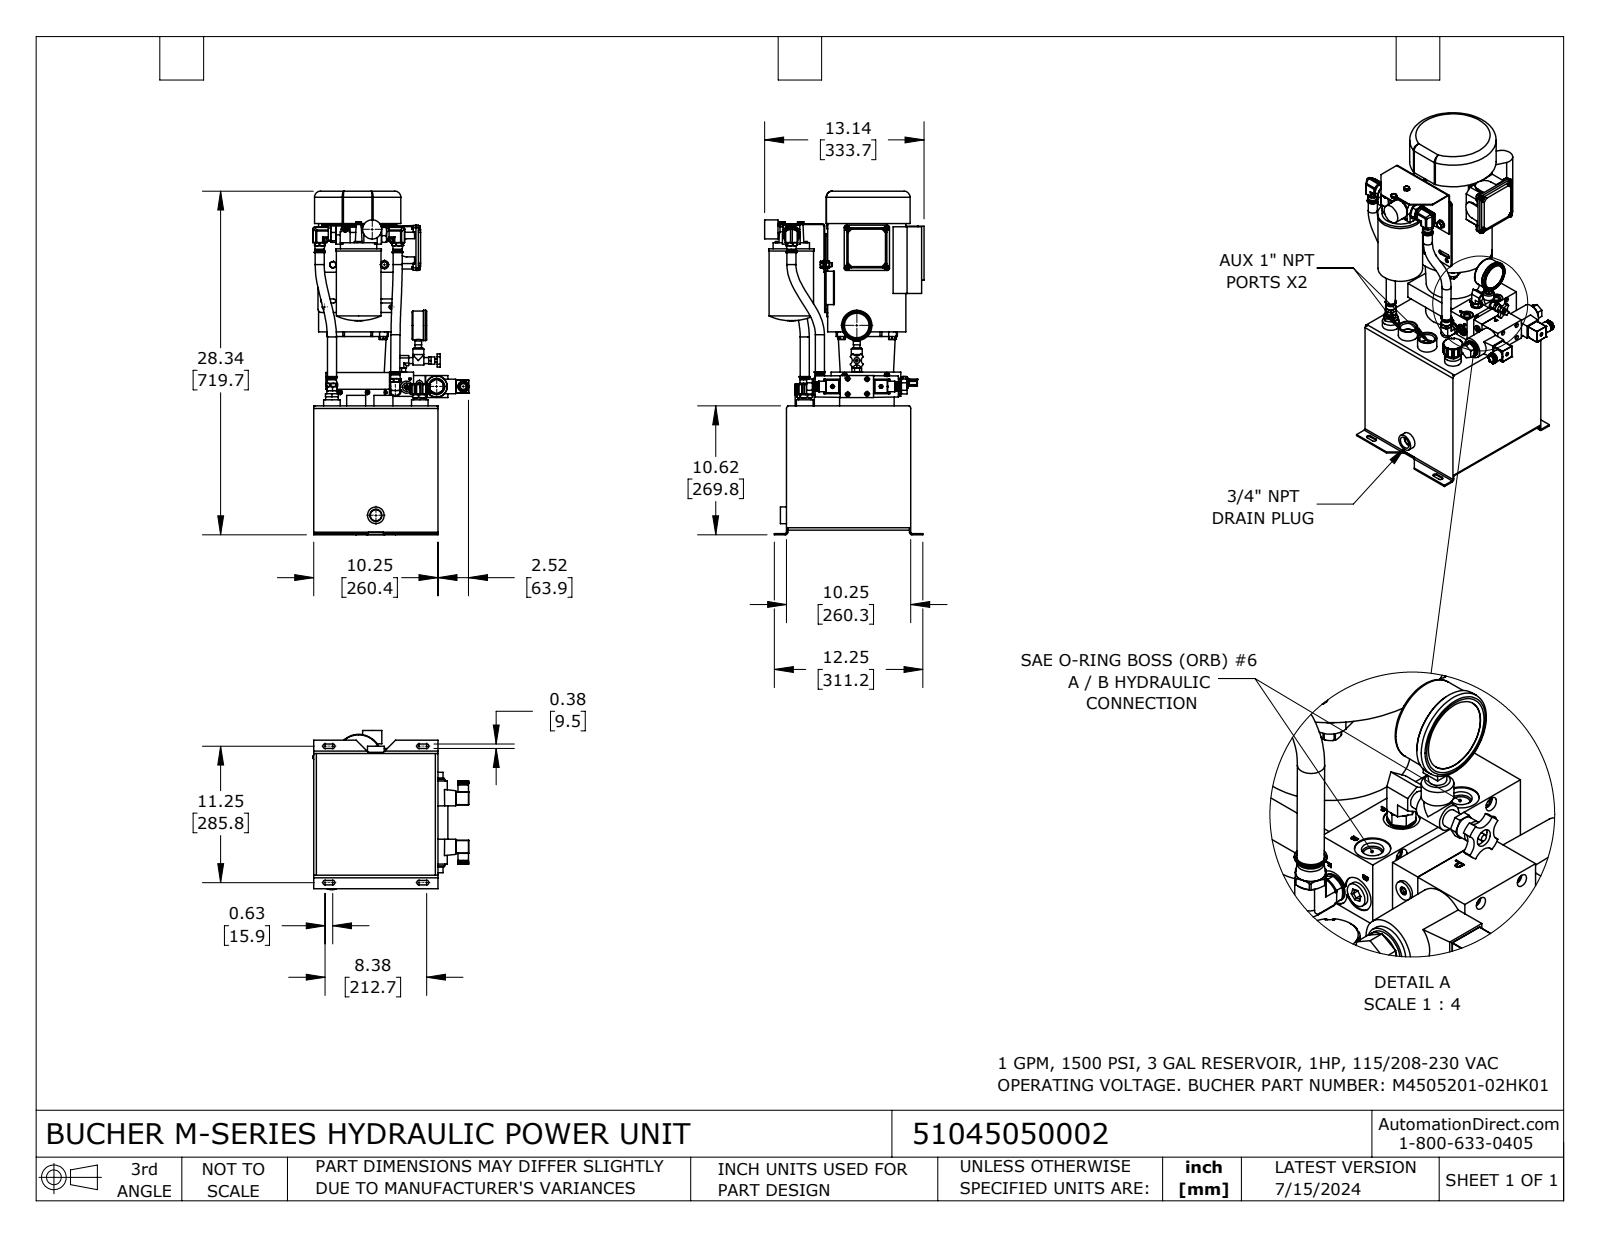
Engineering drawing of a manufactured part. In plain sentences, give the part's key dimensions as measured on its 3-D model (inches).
The part is named "51045050002". Its 3-D file was written by "SolidWorks 2023 (CONFIG_CONTROL_DESIGN)". It is 39 solids with 4372 faces: 1872 planar, 1309 cylindrical and 1191 other. Overall it measures 28.335 by 13.138 by 12.866 inches. Its volume is 771.3 cubic inches and its surface area 2 756 square inches. Round holes: 10 of diameter 1, 9 of diameter 0.25, 8 of diameter 0.469, 8 of diameter 0.511, 6 of diameter 0.225, 6 of diameter 0.339, 6 of diameter 0.5, 5 of diameter 0.281, 5 of diameter 0.391, 4 of diameter 0.17, 4 of diameter 0.197, 4 of diameter 0.203. Round bosses or shafts: 6 of diameter 0.367, 6 of diameter 0.187, 5 of diameter 0.9, 5 of diameter 0.75, 4 of diameter 0.738, 4 of diameter 0.68, 4 of diameter 0.46, 4 of diameter 0.308. Partial cylindrical surfaces (rounded edges, fillets, slot ends): 110 of radius 0.01, 32 of radius 0.02, 24 of radius 0.025, 24 of radius 0.039, 24 of radius 0.05, 13 of radius 0.12, 12 of radius 0.105, 12 of radius 0.169. The main face-to-face distances are 0.105, 0.104, 10.145, 10.144, 10.25, 10.248, 10.041, 10.04, 10.146, 10.041. The hole center spacings are 1.575, 3.268, 4, 5.5, 0.532, 0.533, 0.639, 0.688.
